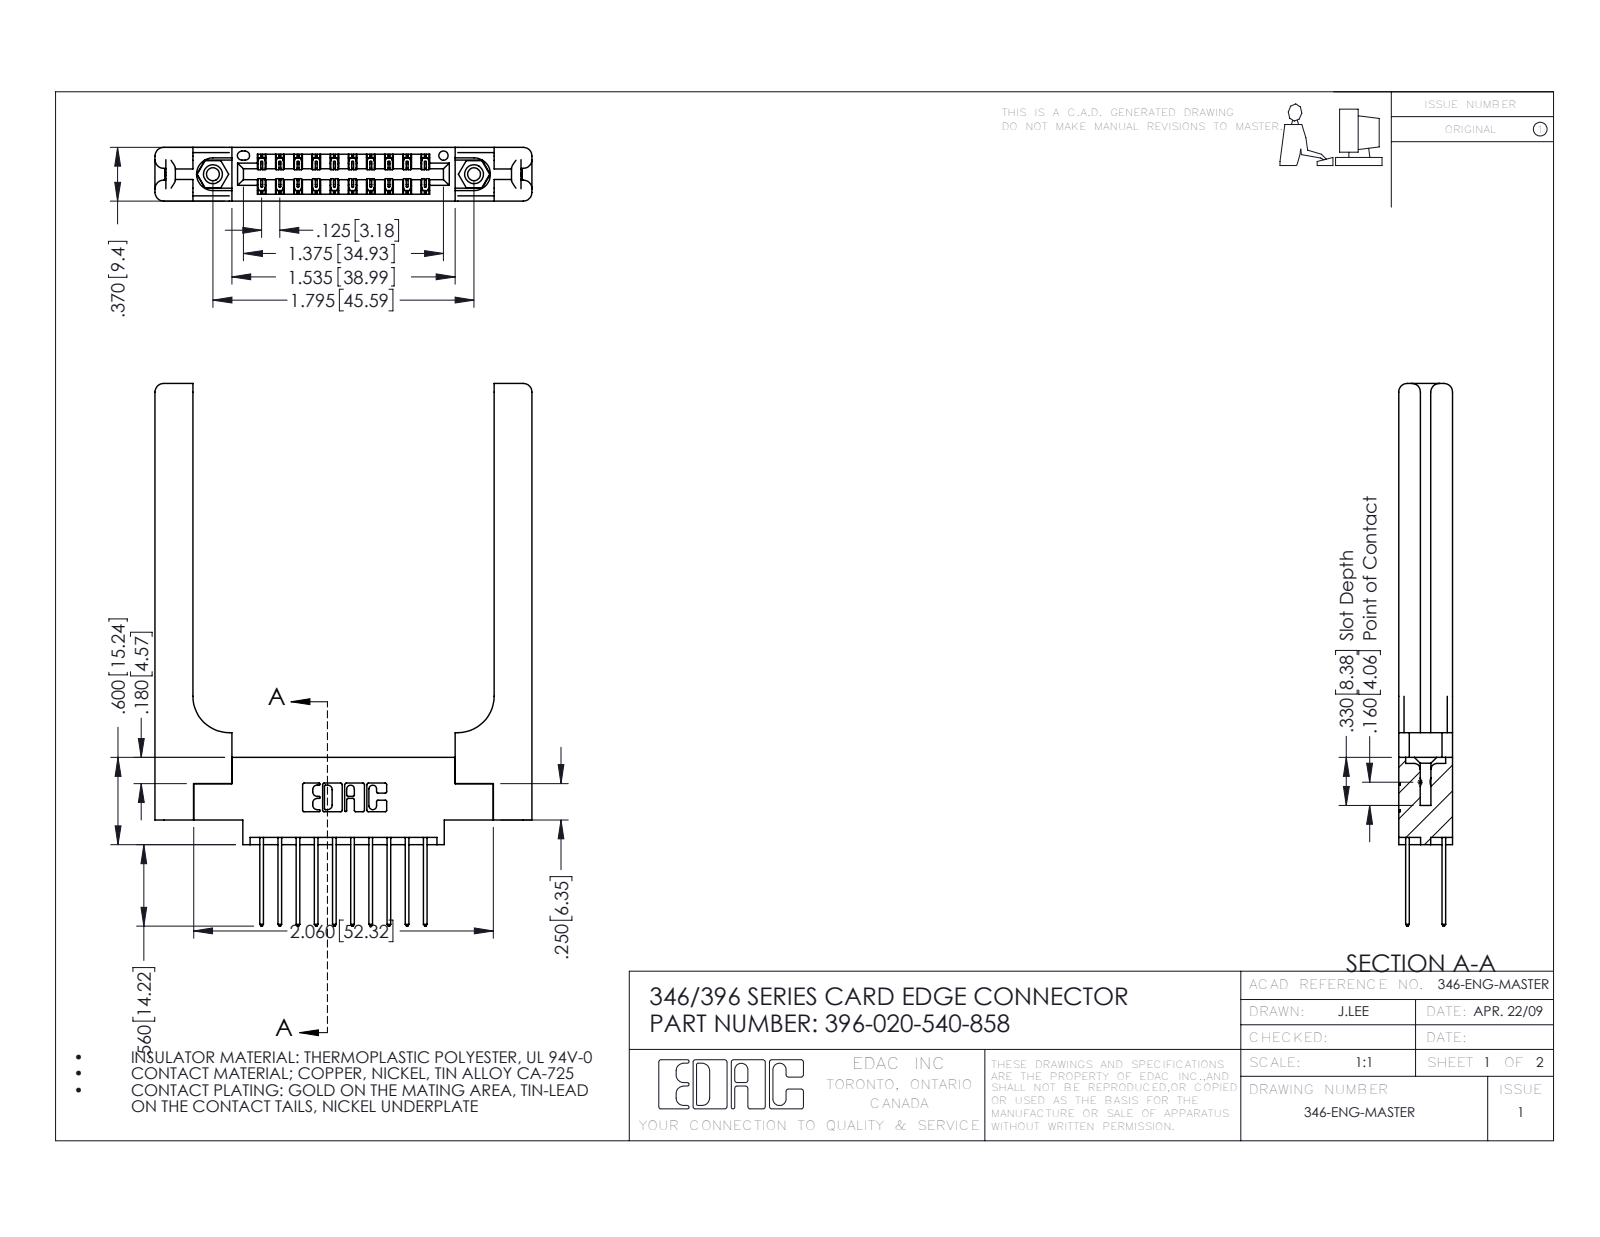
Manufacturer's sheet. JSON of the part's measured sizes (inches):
{"part_name": "346 Part_0.170 Offset - 0.156 Dia-TH; 345-250-001_345-250-001-102; 346-220-058_345-220-058; 345-292-001_345-293-140 (+1 more)", "step_written_by": "SolidWorks 2016 (CONFIG_CONTROL_DESIGN)", "units": "inches", "bodies": {"solids": 25, "faces": 1422, "planar": 928, "cylindrical": 434, "other": 60}, "overall_size": [3.73, 2.591, 0.37], "volume_in3": 0.829, "surface_area_in2": 20.74, "round_holes": [[0.089, 2], [0.125, 2], [0.156, 2], [0.064, 1]], "round_bosses_or_shafts": [[0.155, 2]], "partial_cylinders_radius": [[0.006, 30], [0.01, 22], [0.01, 20], [0.06, 16], [0.007, 6], [0.031, 6], [0.026, 3], [0.014, 2]], "face_to_face_distances": [0.37, 0.15, 0.072, 0.148, 0.048, 0.322, 0.25, 0.102, 0.22, 0.173], "hole_center_spacings": [0.246, 1.59, 1.795]}
